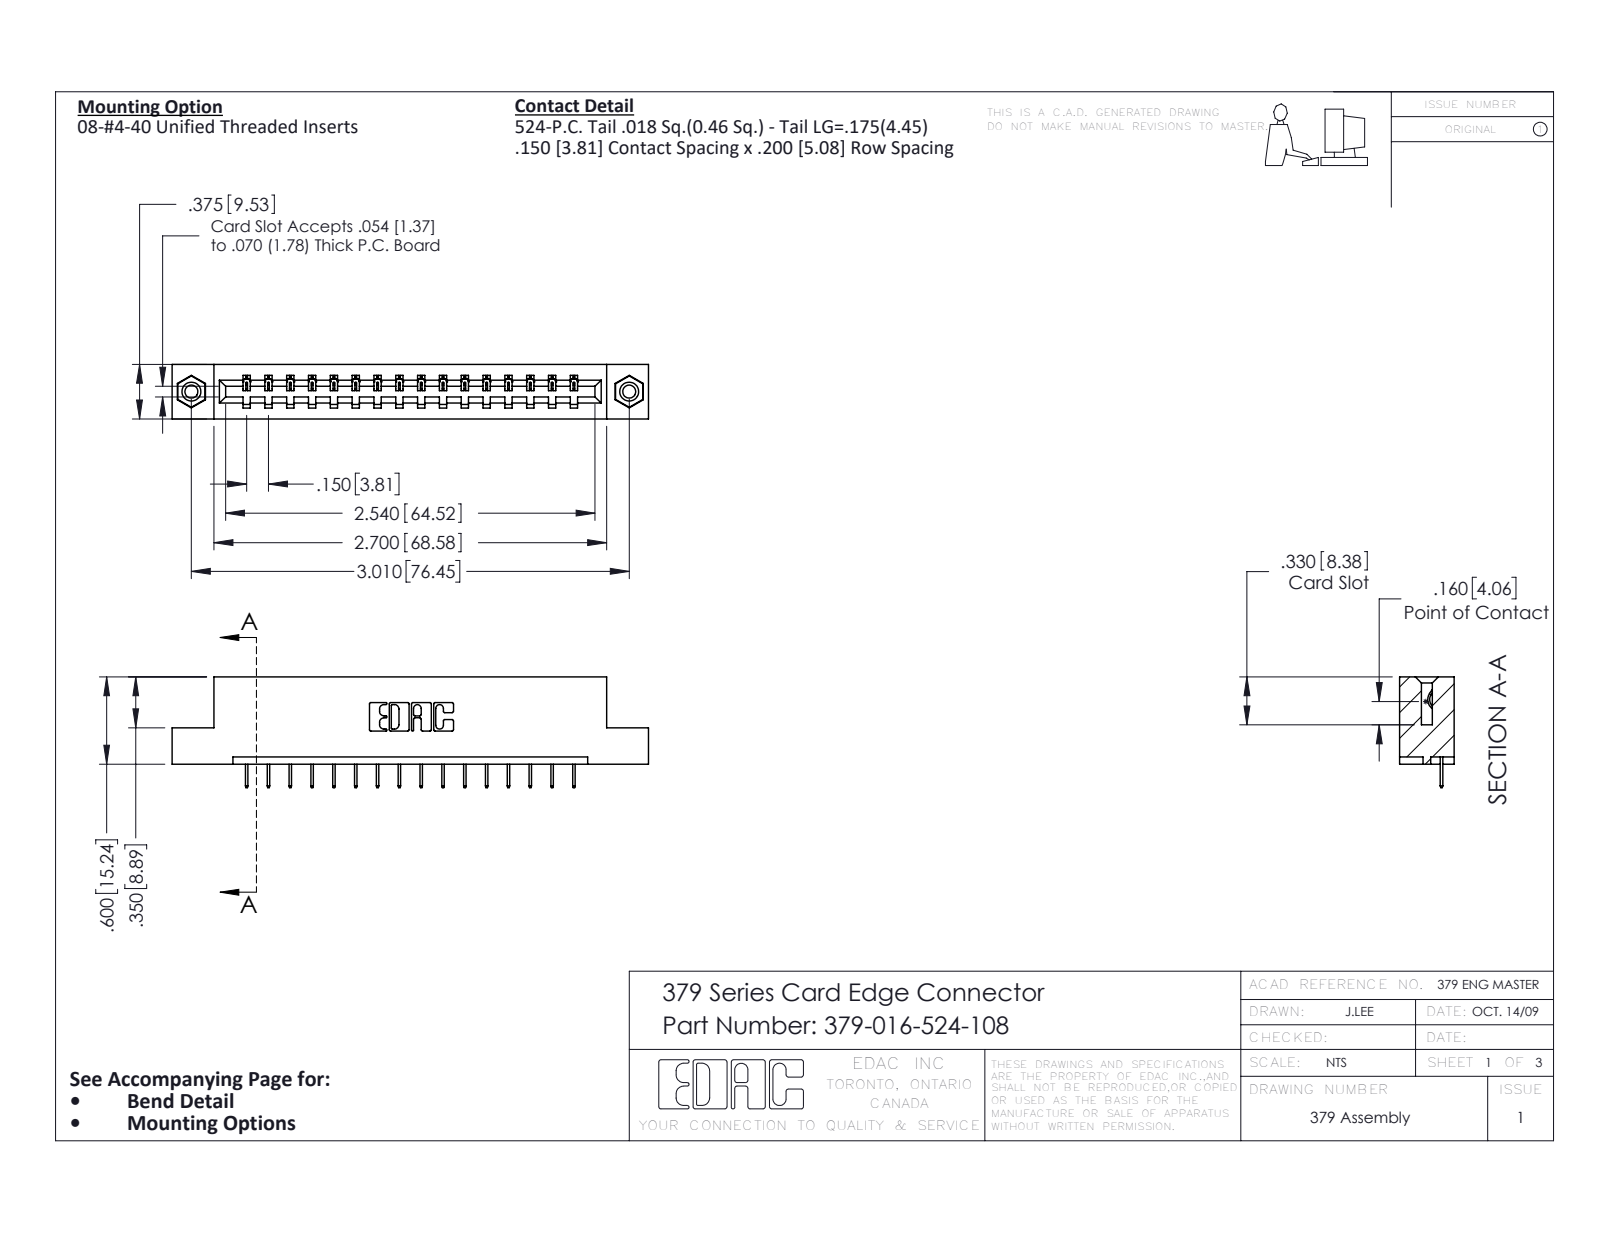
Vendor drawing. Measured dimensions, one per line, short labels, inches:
name: 379-016-524-108; 379 Part_Flush - .156 Dia - TI; 345-292-001_345-293-124; 345-250-001_345-250-003-102
written by: SolidWorks 2020 (CONFIG_CONTROL_DESIGN)
unit: in
bodies: 19 solids, 1166 faces (870 planar, 280 cylindrical, 16 other)
size: 3.275 × 0.762 × 0.375
volume: 0.51 in³; area: 12.76 in²
holes: 2× ⌀0.089, 2× ⌀0.125, 2× ⌀0.156
bosses: 2× ⌀0.155
rounds: 32× R0.006, 22× R0.01, 6× R0.007, 6× R0.031, 3× R0.026, 1× R0.014, 1× R0.022, 1× R0.024
face distances: 0.3, 0.375, 0.075, 0.6, 0.15, 0.225, 0.45, 0.75, 0.2, 0.9
hole spacings: 3.01
